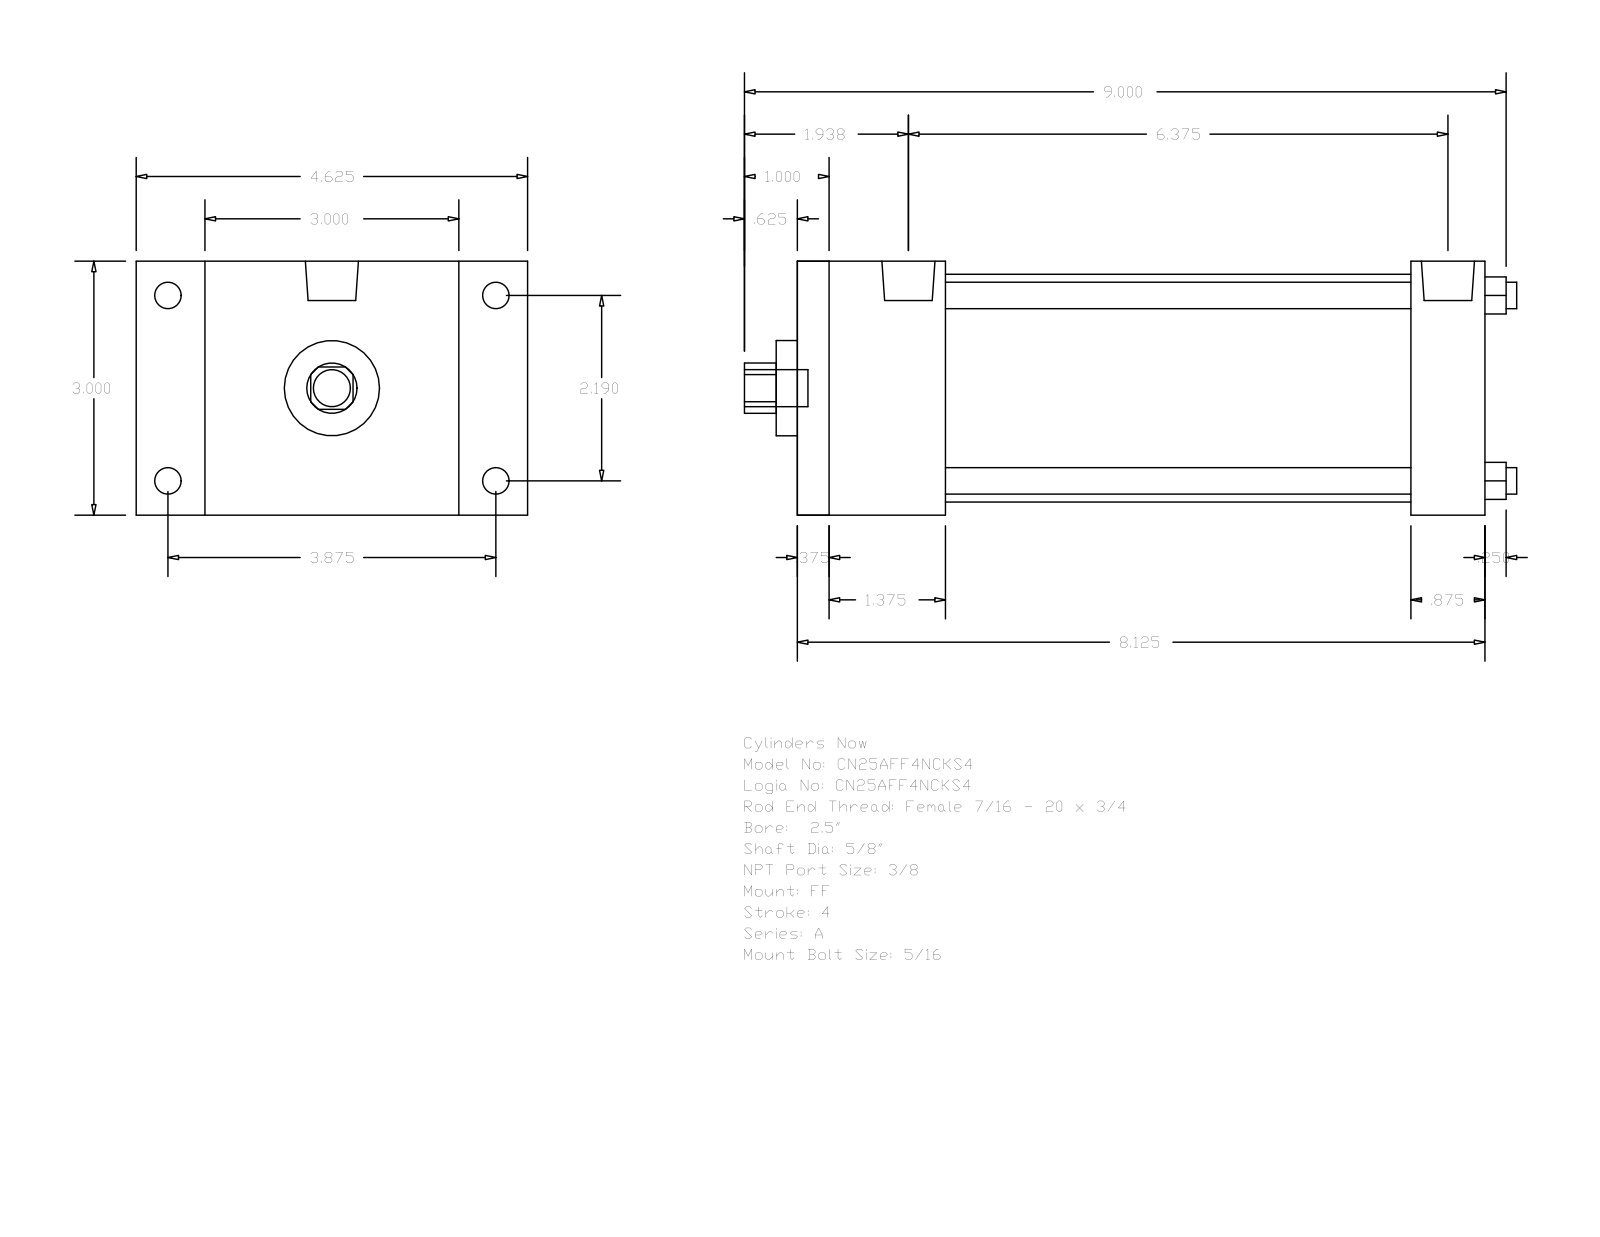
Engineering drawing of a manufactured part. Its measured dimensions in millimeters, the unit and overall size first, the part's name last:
Units: millimetres
Overall size (bounding box): 231.78 × 117.47 × 76.2
Round holes (diameter × count): ⌀7.94 ×4, ⌀15.88 ×1, ⌀28.57 ×1, ⌀68.33 ×1
Round bosses / shafts (diameter × count): ⌀7.94 ×4, ⌀5.56 ×4, ⌀15.93 ×2, ⌀11.11 ×1
Partial cylindrical surfaces — rounded edges, fillets, slot ends (radius × count): R7.54 ×1
Main face-to-face distances: 76.2, 206.37, 9.52, 196.85, 44.45, 184.15, 34.93, 174.63, 139.7, 161.92
Hole centre spacings: 39.33, 55.62, 78.66
Bodies: 0 solids, 92 faces (64 planar, 28 cylindrical, 0 other)
Part name (STEP PRODUCT): A_FF__0250_0.625
STEP written by: GSSL Pune (CONFIG_CONTROL_DESIGN)
